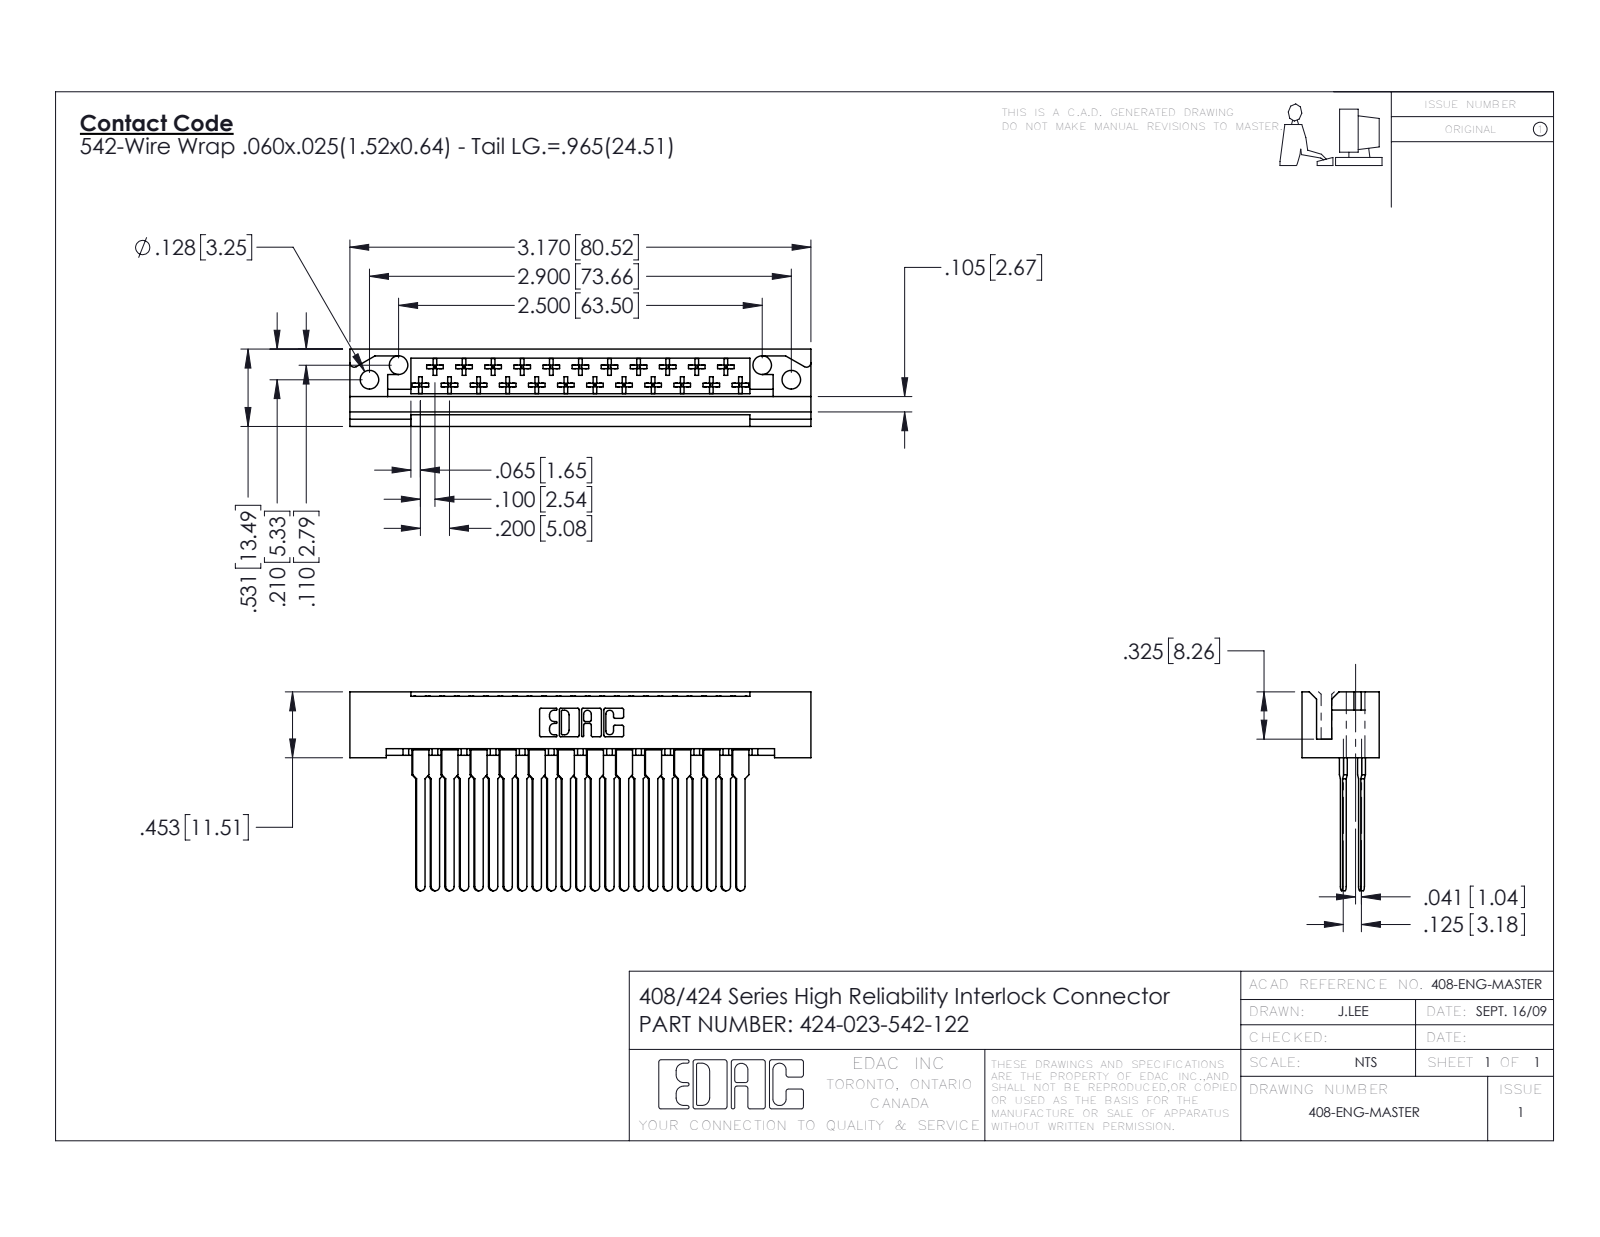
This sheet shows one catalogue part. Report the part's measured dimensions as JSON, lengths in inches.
{"part_name": "424 Part_023; 408-290-001_408-290-142; 424-023-542-122", "step_written_by": "SolidWorks 2016 (CONFIG_CONTROL_DESIGN)", "units": "inches", "bodies": {"solids": 24, "faces": 1364, "planar": 1009, "cylindrical": 263, "other": 92}, "overall_size": [3.17, 1.367, 0.531], "volume_in3": 0.537, "surface_area_in2": 19.71, "round_holes": [[0.128, 4]], "partial_cylinders_radius": [[0.01, 138], [0.02, 25], [0.03, 25], [0.01, 22], [0.007, 6], [0.031, 6], [0.026, 3]], "face_to_face_distances": [0.1, 0.296, 0.025, 0.531, 0.125, 0.104, 0.431, 0.105, 0.326, 0.205], "hole_center_spacings": [0.224, 2.702, 2.5, 2.9]}
